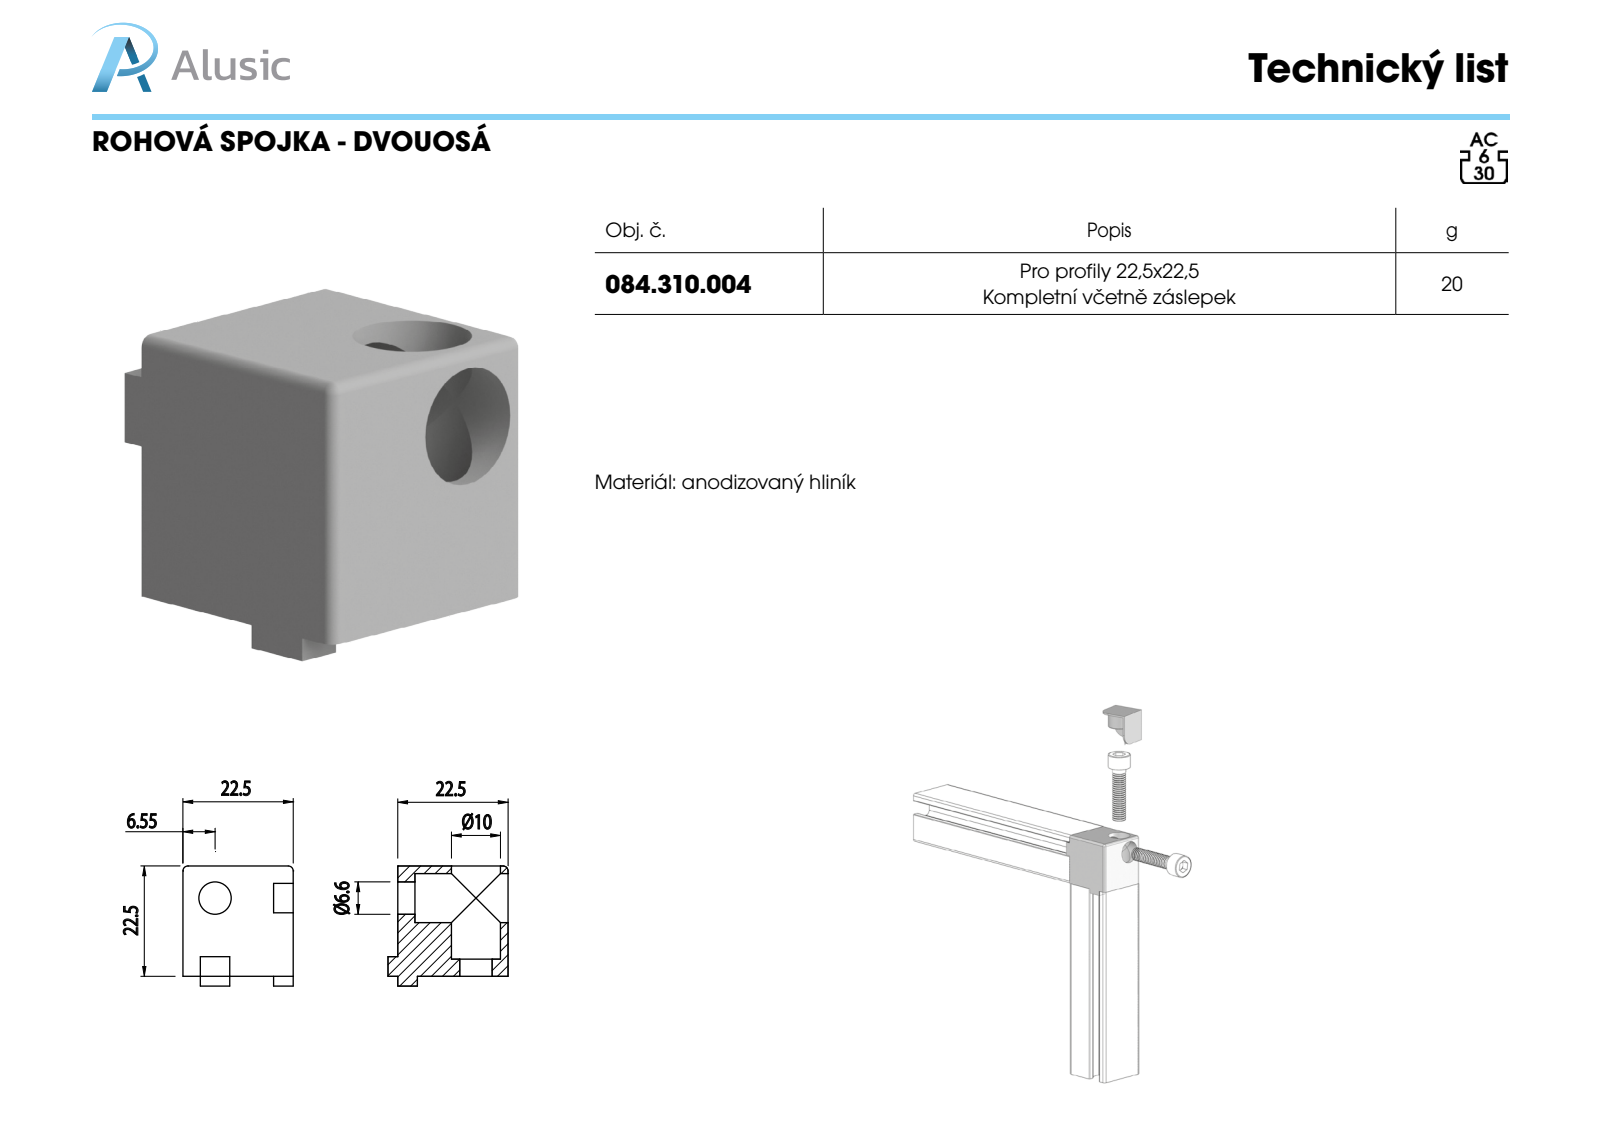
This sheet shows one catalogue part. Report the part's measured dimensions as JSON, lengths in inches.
{"part_name": "084.310.004", "step_written_by": "SolidWorks 2011 (CONFIG_CONTROL_DESIGN)", "units": "inches", "bodies": {"solids": 1, "faces": 45, "planar": 26, "cylindrical": 17, "other": 2}, "overall_size": [0.965, 0.965, 0.886], "volume_in3": 0.549, "surface_area_in2": 6.123, "round_holes": [[0.26, 2], [0.394, 2]], "partial_cylinders_radius": [[0.039, 5]], "face_to_face_distances": [0.886, 0.079, 0.965, 0.217, 0.138, 0.748, 0.236, 0.589, 0.157, 0.728]}
